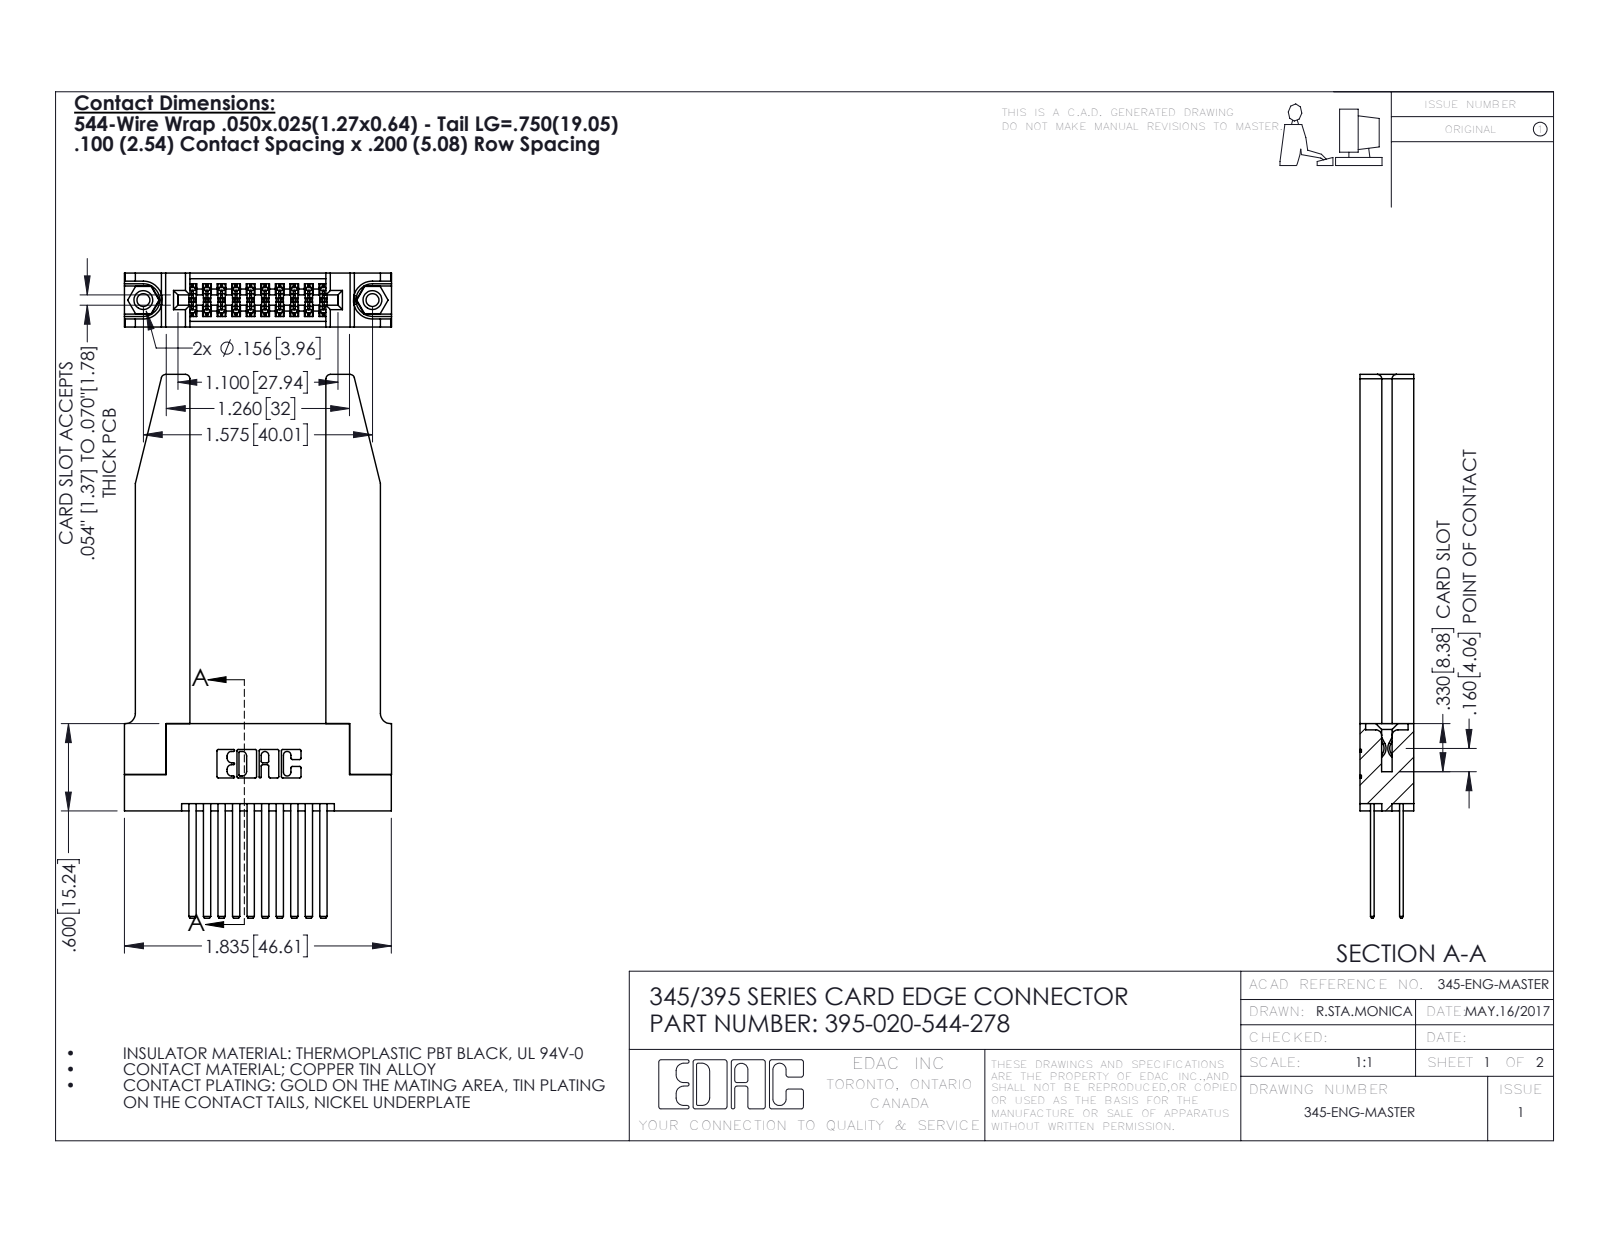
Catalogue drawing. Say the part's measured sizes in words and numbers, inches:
The part is named "345-220-078_345-220-078; 345-292-001_345-293-144; 345 Part_Flush Mounting Lugs - 0.156 Dia-TH; 345-250-001_345-250-001-102 (+1 more)". Its 3-D file was written by "SolidWorks 2016 (CONFIG_CONTROL_DESIGN)". It is 25 solids with 1240 faces: 802 planar, 386 cylindrical and 52 other. Overall it measures 3.737 by 1.836 by 0.37 inches. Its volume is 0.75 cubic inches and its surface area 21.25 square inches. Round holes: 2 of diameter 0.089, 2 of diameter 0.125, 2 of diameter 0.156, 1 of diameter 0.064. Round bosses or shafts: 2 of diameter 0.155. Partial cylindrical surfaces (rounded edges, fillets, slot ends): 30 of radius 0.006, 22 of radius 0.01, 8 of radius 0.03, 6 of radius 0.007, 6 of radius 0.031, 3 of radius 0.026, 2 of radius 0.014, 2 of radius 0.019. The main face-to-face distances are 0.37, 0.072, 0.298, 0.2, 0.098, 0.272, 0.025, 0.225, 0.148, 0.15. The hole center spacings are 0.27, 1.344, 1.575.
